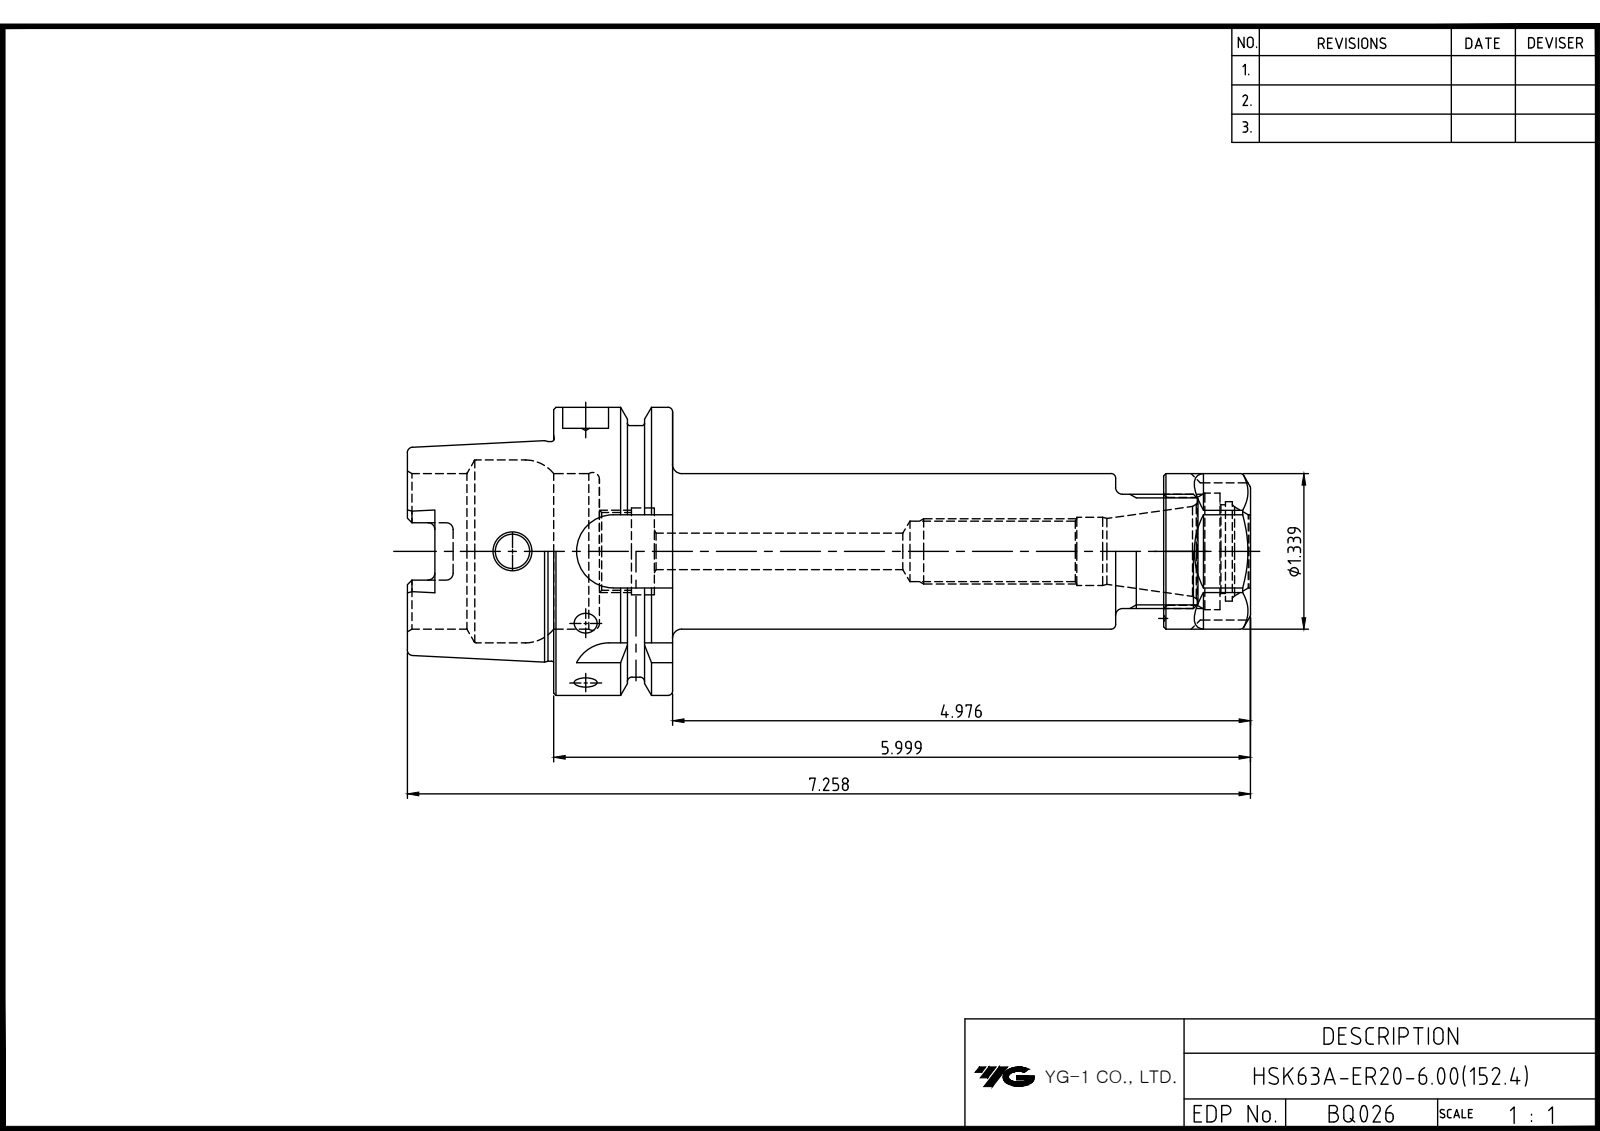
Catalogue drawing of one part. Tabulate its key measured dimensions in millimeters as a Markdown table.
| quantity | value |
| --- | --- |
| part name | HSK63A-ER20-152.4; LO-HSK63A-ER20-152.4; ER20NUT |
| STEP written by | Autodesk Inventor 2024 (AUTOMOTIVE_DESIGN) |
| units | millimeters |
| bodies | 2 solids, 149 faces (61 planar, 41 cylindrical, 47 other) |
| overall size | 184.4 × 63 × 63 |
| volume | 173 299 mm³ |
| surface area | 43 326 mm² |
| round holes (diameter × count) | 7.5 × 1, 8.4 × 1, 10 × 1, 12.57 × 1, 14.9 × 1, 16 × 1, 16.92 × 1, 18.4 × 1, 19 × 1, 21.76 × 1, 23.5 × 1, 25.5 × 1 |
| round bosses / shafts (diameter × count) | 63 × 1, 55 × 1, 48.04 × 1, 25 × 1 |
| partial cylindrical surfaces (radius × count) | 1.5 × 6, 2.88 × 4, 8 × 4 |
| main face-to-face distances | 26, 10, 16, 142.4, 126.4, 30, 32, 152.4, 11.5, 19 |
